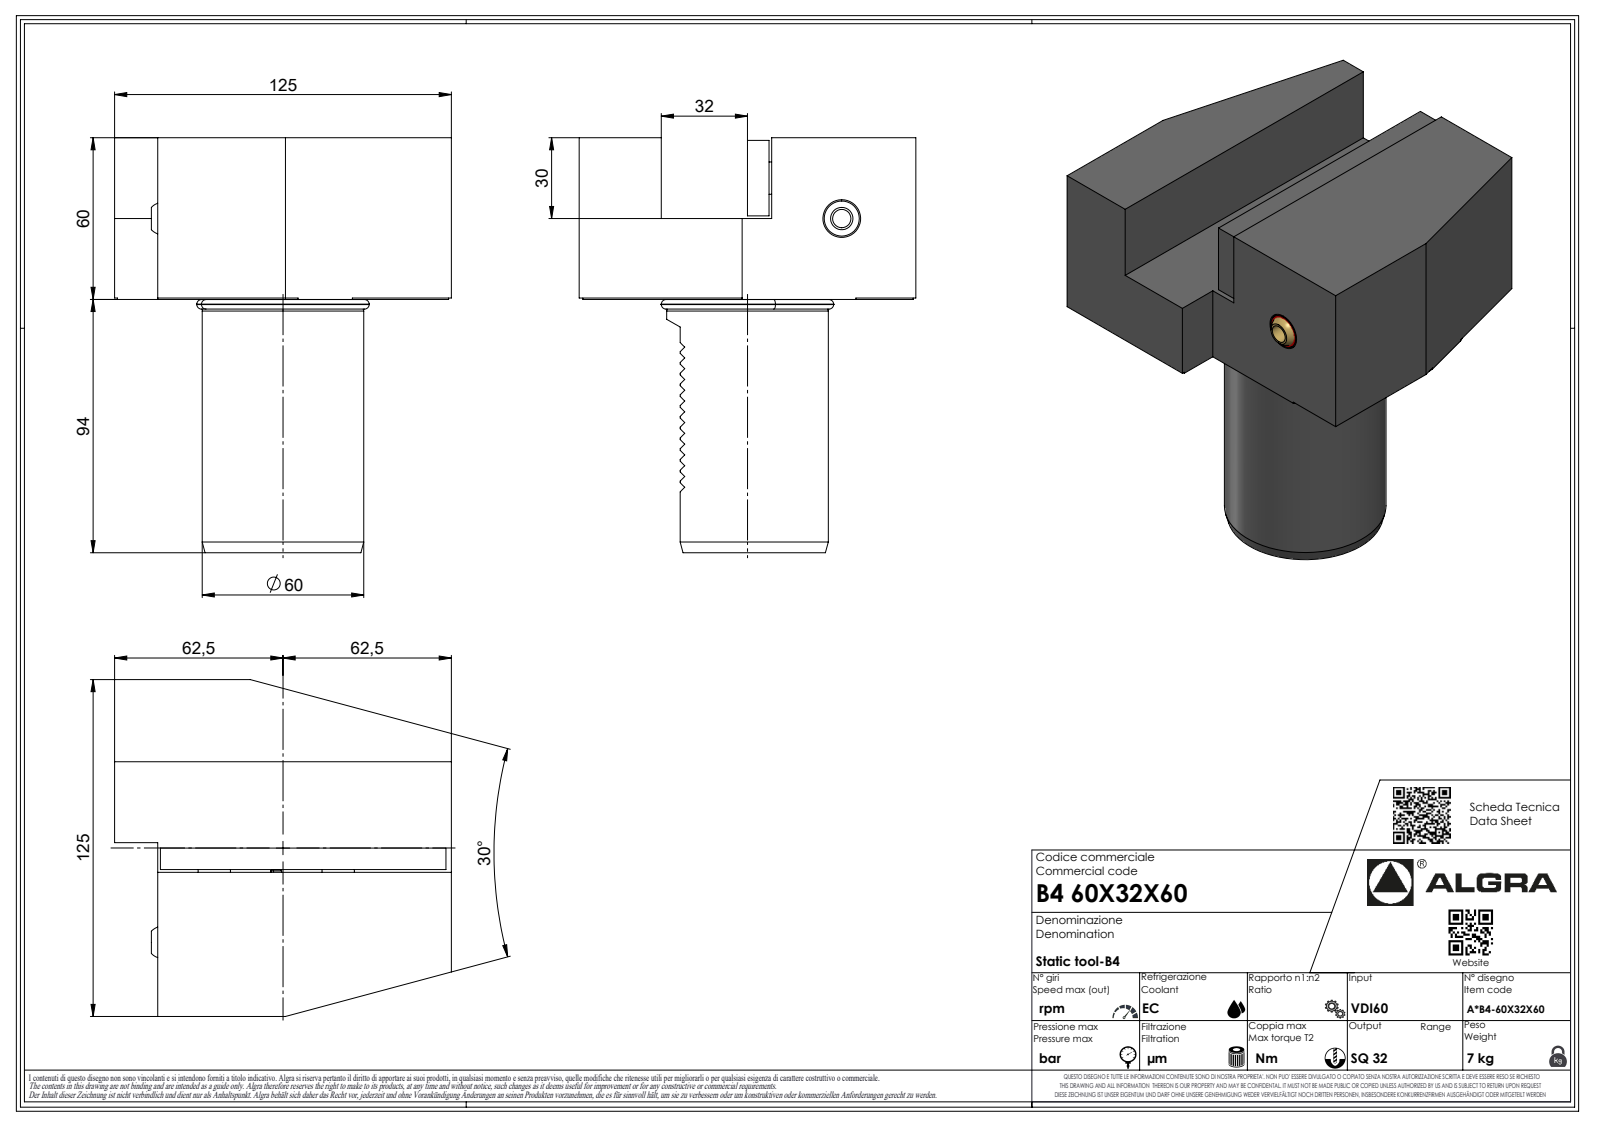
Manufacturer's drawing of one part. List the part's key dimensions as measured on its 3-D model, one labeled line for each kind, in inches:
Part name (STEP PRODUCT): B460X32X60
STEP written by: SolidWorks 2023 (AUTOMOTIVE_DESIGN)
Units: inches
Bodies: 1 solid, 349 faces (238 planar, 34 cylindrical, 77 other)
Overall size (bounding box): 6.063 × 4.921 × 4.921
Volume: 56.78 in³ · Surface area: 132.4 in²
Round holes (diameter × count): ⌀0.083 ×1
Round bosses / shafts (diameter × count): ⌀0.472 ×2, ⌀2.527 ×1, ⌀2.362 ×1, ⌀0.251 ×1, ⌀0.157 ×1, ⌀0.067 ×1
Partial cylindrical surfaces — rounded edges, fillets, slot ends (radius × count): R0.013 ×7, R0.02 ×7, R0.146 ×7, R0.008 ×1, R2.421 ×1
Main face-to-face distances: 1.181, 2.362, 4.921, 2.461, 3.72, 0.039, 1.201, 4.291, 1.614, 2.815
